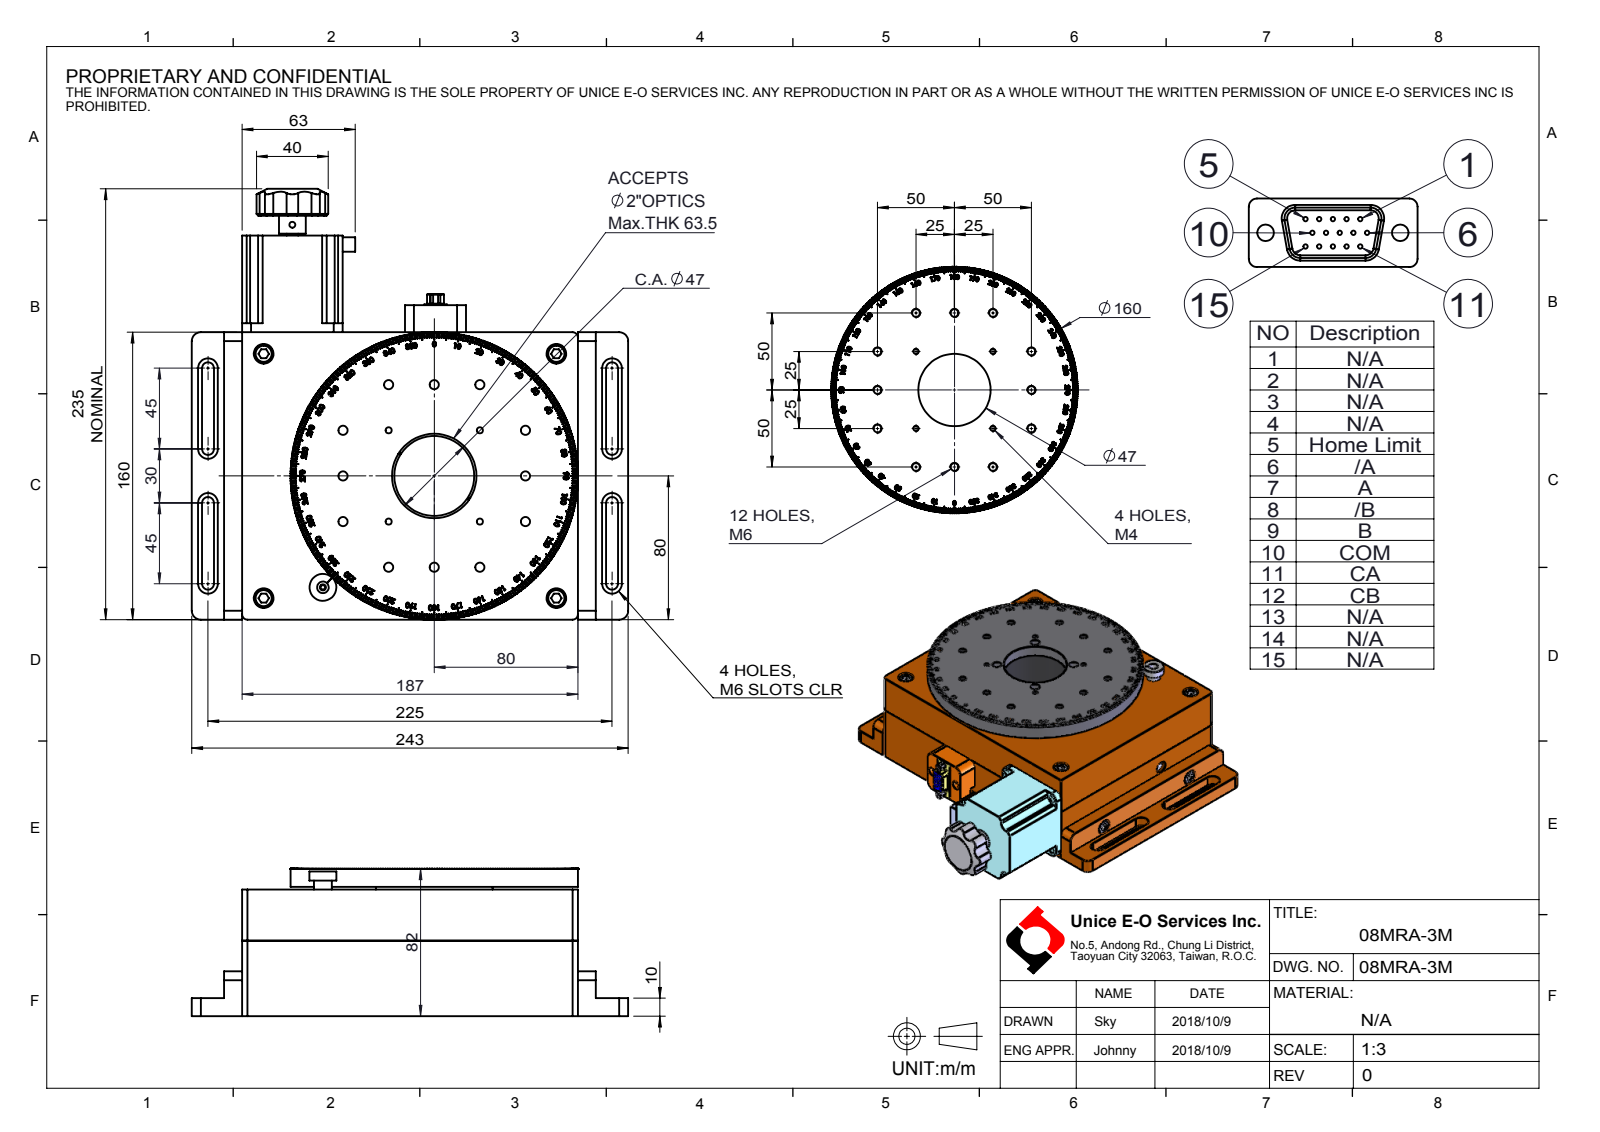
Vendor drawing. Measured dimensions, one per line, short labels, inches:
name: 08MRA-3M
written by: SolidWorks 2016 (AUTOMOTIVE_DESIGN)
unit: in
bodies: 0 solids, 1057 faces (734 planar, 233 cylindrical, 90 other)
size: 9.567 × 9.441 × 3.228
holes: 12× ⌀0.201, 10× ⌀0.031, 7× ⌀0.256, 6× ⌀0.134, 6× ⌀0.433, 4× ⌀0.136, 4× ⌀0.177, 2× ⌀0.059, 2× ⌀0.098, 2× ⌀0.197, 1× ⌀0.039, 1× ⌀0.354
bosses: 3× ⌀0.394, 2× ⌀0.591, 1× ⌀6.299, 1× ⌀3.346
rounds: 14× R0.197, 8× R0.13, 8× R0.157, 8× R0.217, 8× R0.292, 7× R0.02, 4× R0.059, 4× R0.079
face distances: 0.394, 2.776, 2.835, 0.059, 3.228, 0.453, 7.362, 6.299, 2.736, 8.858
hole spacings: 2.236, 1, 1.414, 3.162, 3.606, 2, 0.112, 0.1
